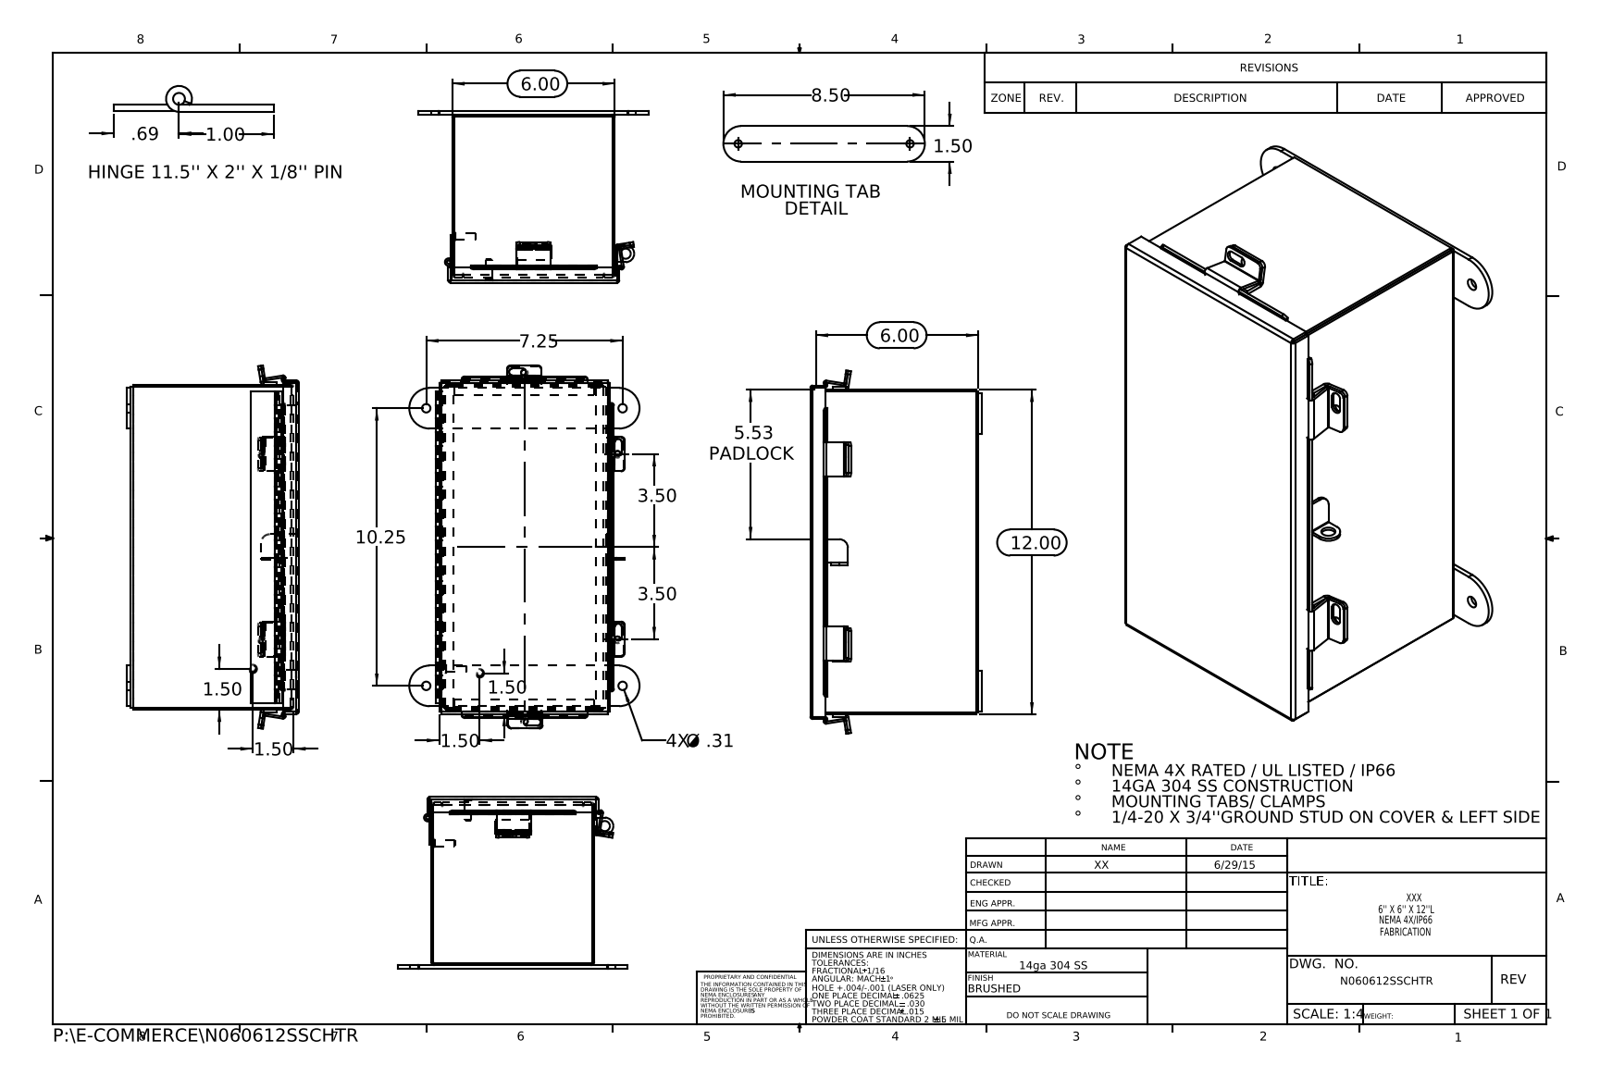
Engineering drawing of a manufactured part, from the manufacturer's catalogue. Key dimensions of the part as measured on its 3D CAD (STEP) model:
Part name (STEP PRODUCT): N060612SSCHTR; N060612SSCHTR JIC Enclosure Template; N060612SSCHTR Mounting Bracket; HW-CLH-JH-20154 (+8 more)
STEP written by: SolidWorks 2015 (CONFIG_CONTROL_DESIGN)
Units: inches
Bodies: 19 solids, 624 faces (393 planar, 211 cylindrical, 20 other)
Overall size (bounding box): 13.407 × 8.5 × 6.337
Volume: 35.09 in³ · Surface area: 926.2 in²
Round holes (diameter × count): ⌀0.25 ×4, ⌀0.313 ×4, ⌀0.125 ×1, ⌀0.375 ×1
Round bosses / shafts (diameter × count): ⌀0.315 ×2, ⌀0.236 ×2, ⌀0.273 ×1, ⌀0.25 ×1
Partial cylindrical surfaces — rounded edges, fillets, slot ends (radius × count): R0.125 ×14, R0.009 ×12, R0.013 ×11, R0.088 ×11, R0.133 ×8, R0.083 ×6, R0.1 ×6, R0.75 ×4
Main face-to-face distances: 0.075, 5.925, 6.128, 6, 5.85, 6.203, 6.053, 11.925, 11.85, 12
Hole centre spacings: 7.25, 10.25, 12.555, 6.543, 6.85
